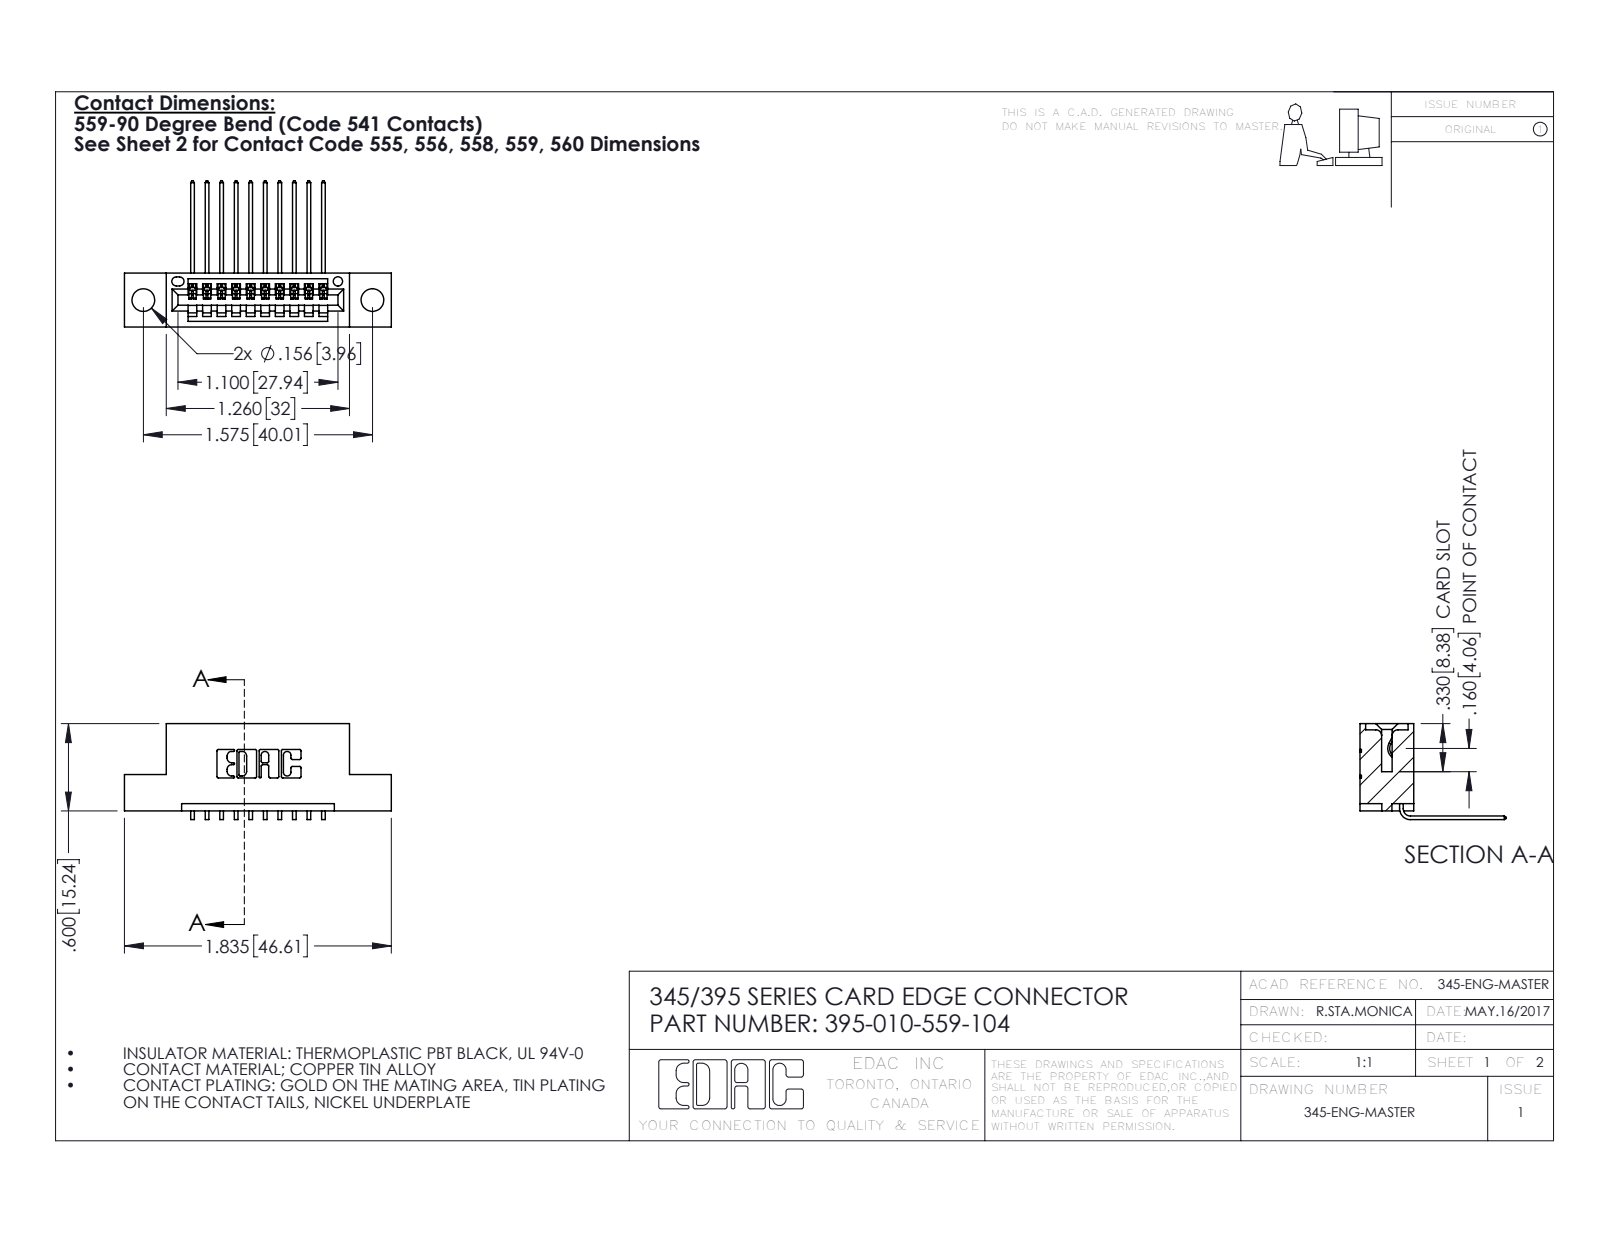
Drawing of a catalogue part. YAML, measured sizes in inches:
part_name: "395-010-559-104; 345 Part_Flush Mounting Lugs - 0.156 Dia-TH; 345-292-001_558 559 Tail - 1"
step_written_by: "SolidWorks 2016 (CONFIG_CONTROL_DESIGN)"
units: inches
bodies: {solids: 11, faces: 726, planar: 500, cylindrical: 226, other: 0}
overall_size: [1.835, 1.005, 0.659]
volume: 0.251
surface_area: 7.799
round_holes:
  - {diameter: 0.156, count: 2}
  - {diameter: 0.064, count: 1}
partial_cylinders:
  - {radius: 0.01, count: 22}
  - {radius: 0.006, count: 20}
  - {radius: 0.007, count: 6}
  - {radius: 0.031, count: 6}
  - {radius: 0.026, count: 3}
  - {radius: 0.031, count: 2}
  - {radius: 0.04, count: 2}
  - {radius: 0.014, count: 1}
face_to_face_distances: [0.2, 0.37, 0.298, 0.072, 0.1, 0.6, 0.098, 0.272, 0.025, 0.06]
hole_center_spacings: [0.27, 1.344, 1.575]
